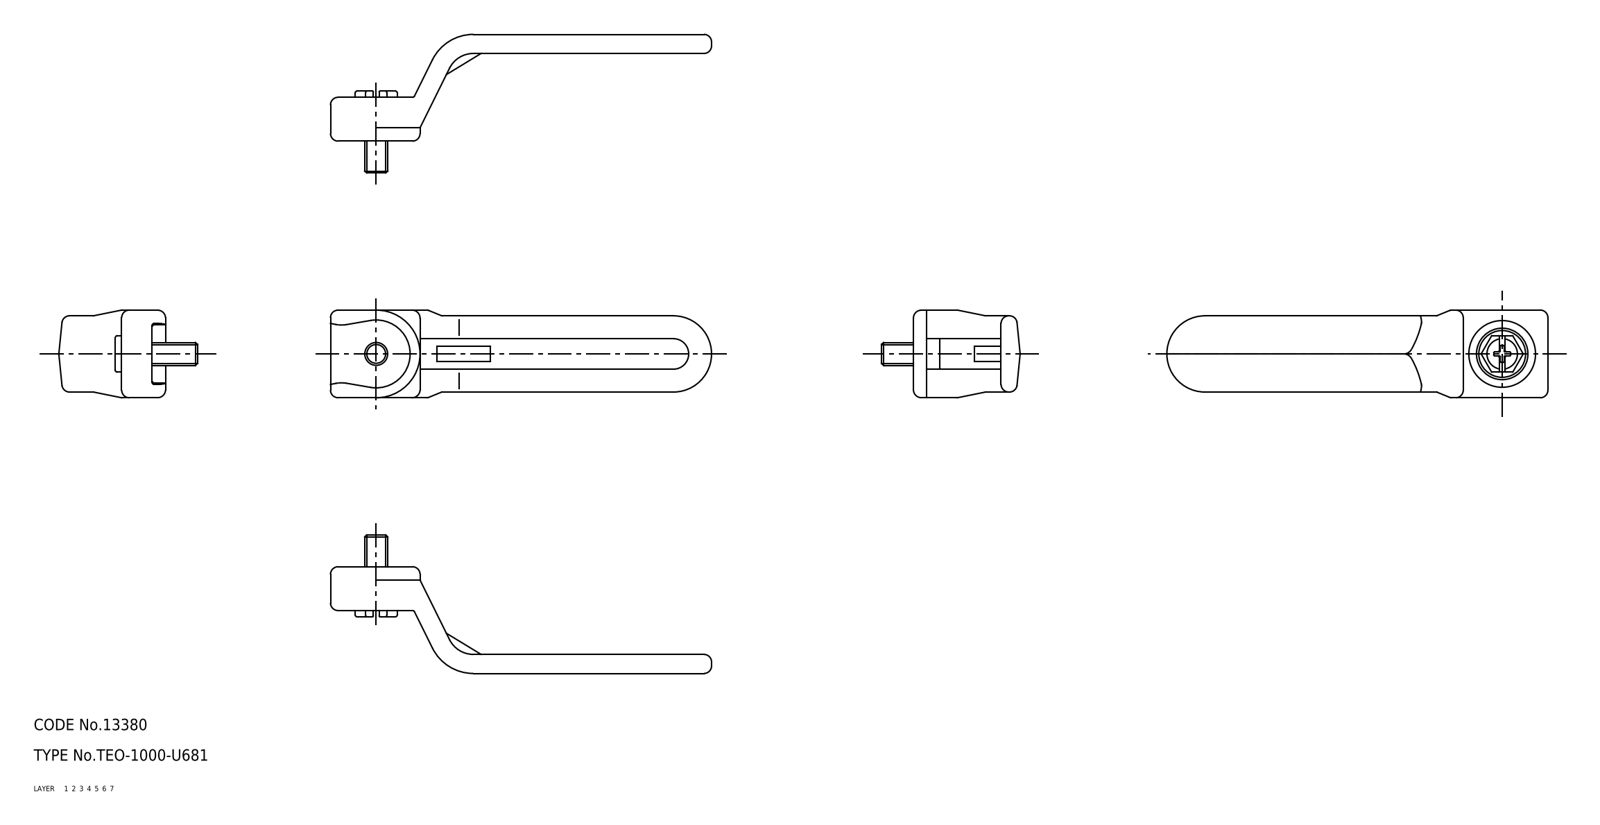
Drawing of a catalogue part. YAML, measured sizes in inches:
part_name: "screw; handle; TEO_1000_U681_9865_36"
step_written_by: "CADfix (AUTOMOTIVE_DESIGN)"
units: inches
bodies: {solids: 2, faces: 207, planar: 0, cylindrical: 0, other: 207}
overall_size: [3.937, 1.431, 0.906]
volume: 0.693
surface_area: 11.18
